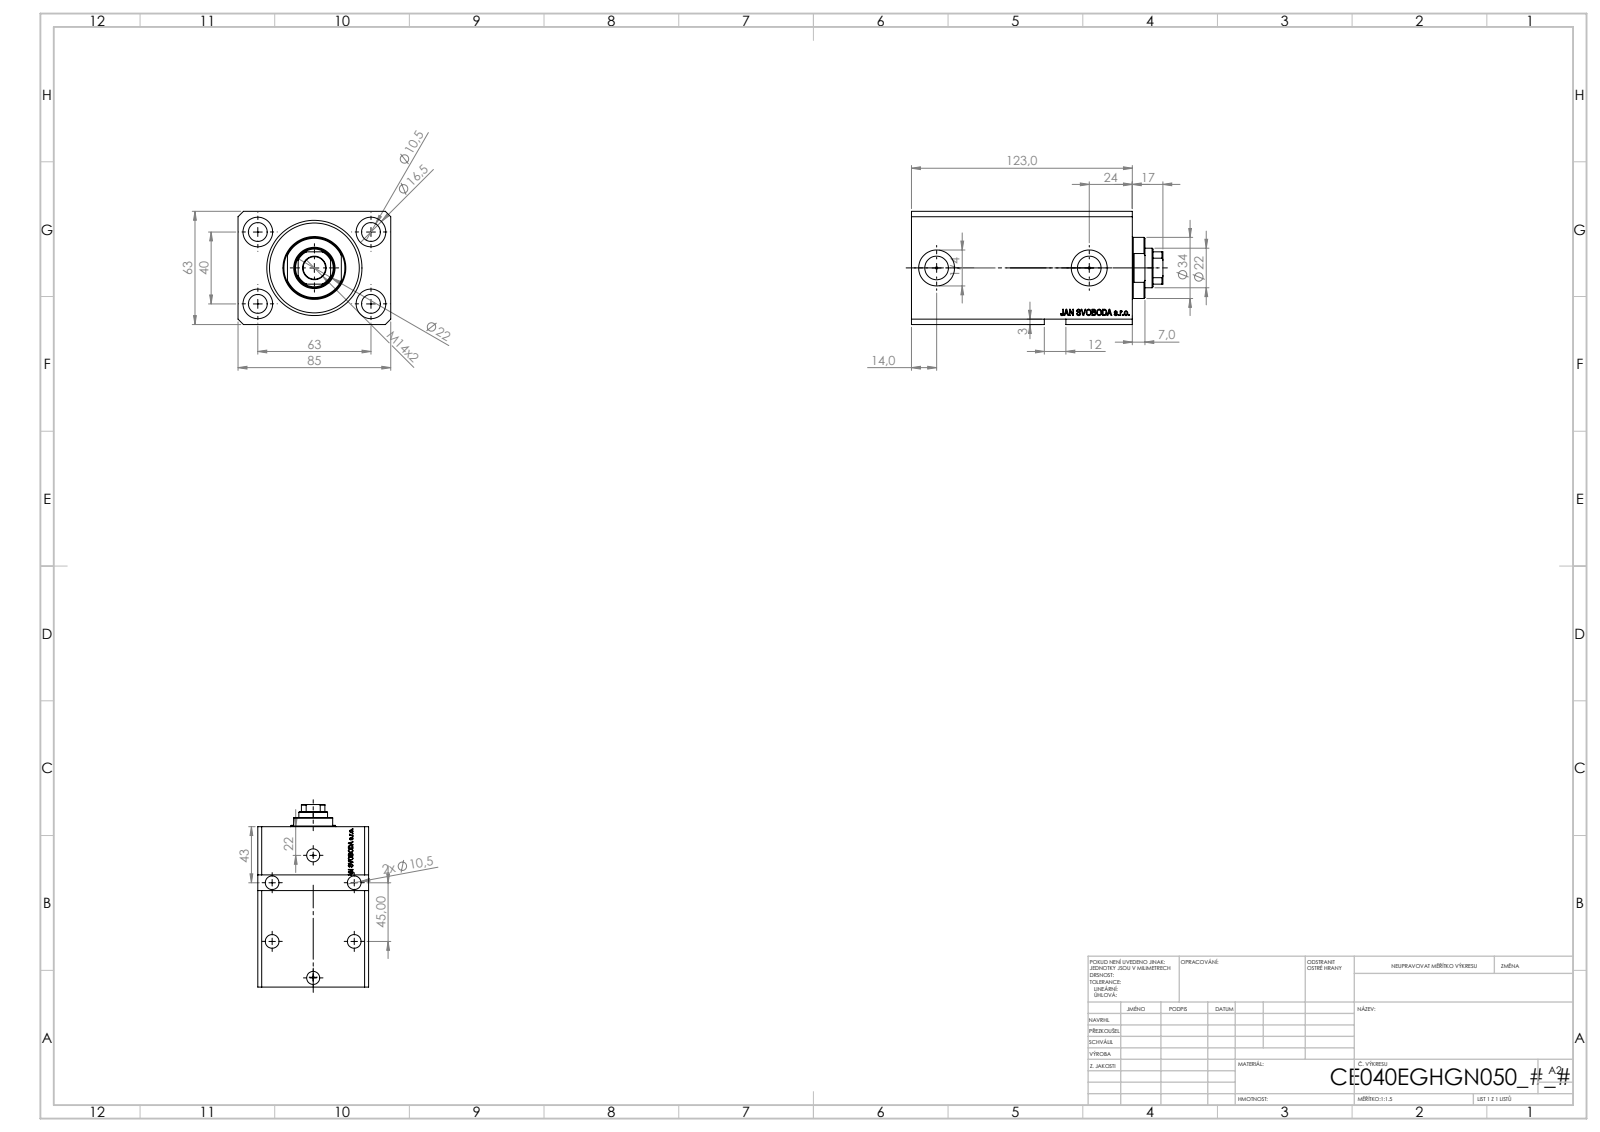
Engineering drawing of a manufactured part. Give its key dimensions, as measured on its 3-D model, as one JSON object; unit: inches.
{"part_name": "V250CE_E_Body; V250CE_VC_E; V250CE_C_VCP", "step_written_by": "SolidWorks 2019 (CONFIG_CONTROL_DESIGN)", "units": "inches", "bodies": {"solids": 3, "faces": 937, "planar": 459, "cylindrical": 104, "other": 374}, "overall_size": [5.512, 3.346, 2.48], "volume_in3": 33.12, "surface_area_in2": 167, "round_holes": [[0.413, 8], [0.049, 4], [0.65, 4], [0.394, 2], [0.518, 2], [0.787, 2], [0.492, 1], [0.866, 1], [1.575, 1], [2.087, 1]], "round_bosses_or_shafts": [[1.339, 1]], "partial_cylinders_radius": [[0.413, 1]], "face_to_face_distances": [2.48, 3.346, 4.843, 0.669, 4.173, 0.449, 3.724, 4.394, 2.205, 0.433], "hole_center_spacings": [1.469, 2.48, 1.491, 1.575, 1.646, 1.659, 1.772, 2.879]}
